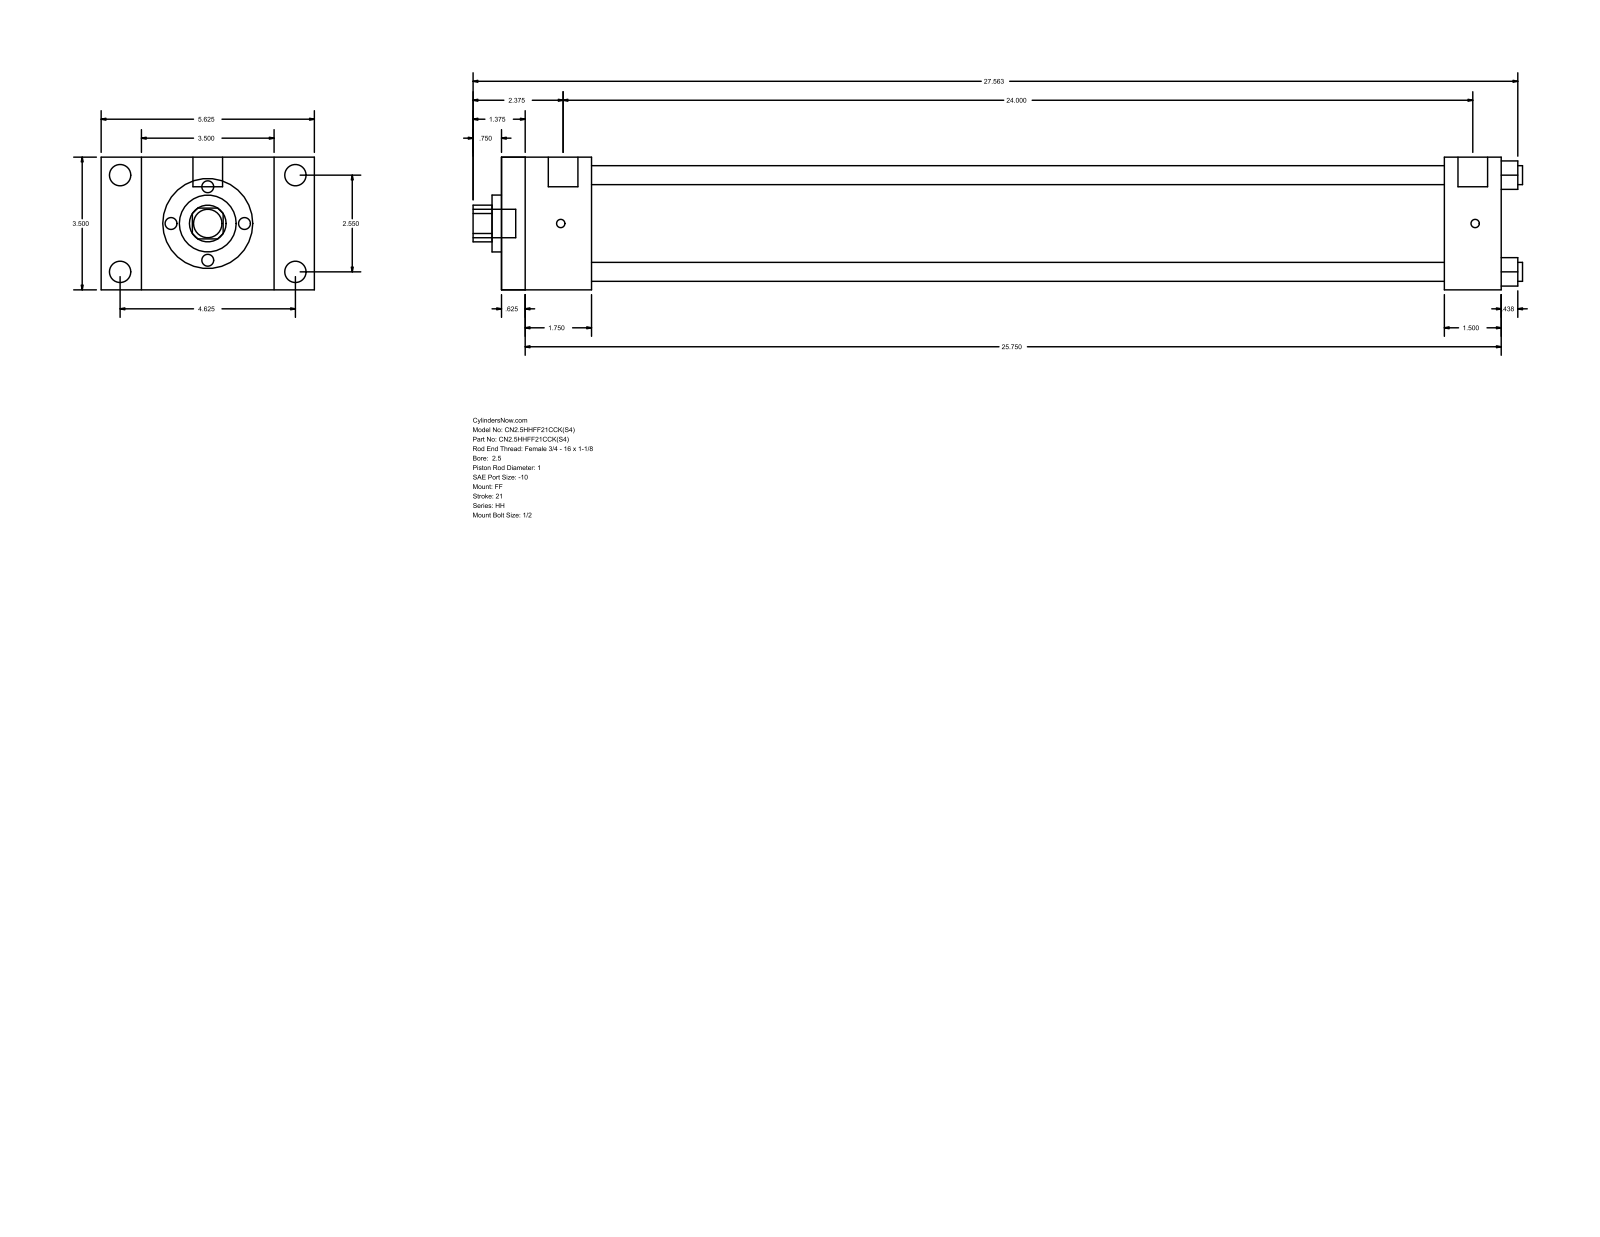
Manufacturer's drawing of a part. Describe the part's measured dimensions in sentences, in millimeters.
The part is named "HH_FF__0250_1". Its 3-D file was written by "GSSL Pune (CONFIG_CONTROL_DESIGN)". It is 0 solids with 92 faces: 64 planar, 28 cylindrical and 0 other. Overall it measures 703.26 by 142.88 by 88.9 millimeters. Round holes: 4 of diameter 12.7, 1 of diameter 25.4, 1 of diameter 38.1, 1 of diameter 73.03. Round bosses or shafts: 4 of diameter 14.3, 4 of diameter 5.56, 2 of diameter 19.84, 1 of diameter 19.05. Partial cylindrical surfaces (rounded edges, fillets, slot ends): 1 of radius 12.29. The main face-to-face distances are 88.9, 669.93, 15.87, 654.06, 60.33, 44.46, 609.6, 631.83, 615.96, 571.5. The hole center spacings are 45.79, 64.76, 91.58.
